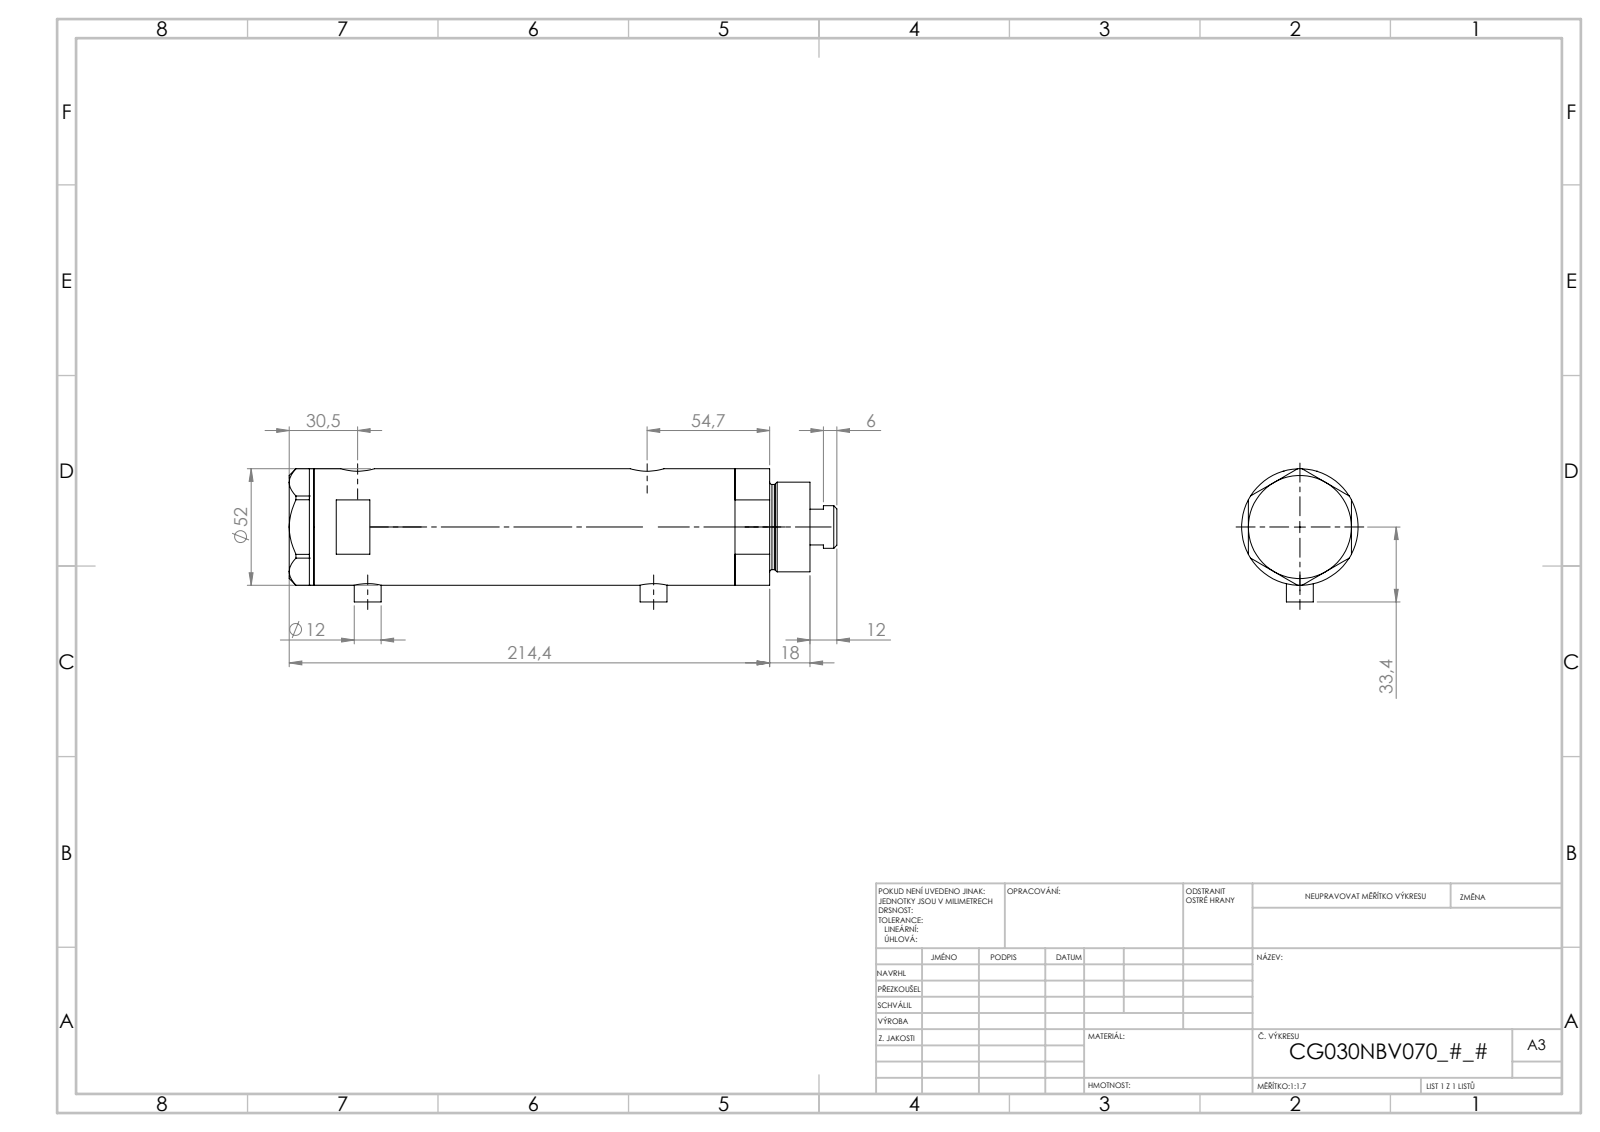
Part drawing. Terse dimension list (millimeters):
name: V270CG_FRONT; V270CG_BACK; V270CG_MIDDLE; V270CG_VC
written by: SolidWorks 2019 (CONFIG_CONTROL_DESIGN)
unit: mm
bodies: 4 solids, 134 faces (65 planar, 49 cylindrical, 20 other)
size: 244.4 × 59.4 × 52
volume: 446 635 mm³; area: 96 990 mm²
holes: 2× ⌀9.73, 2× ⌀12.5, 2× ⌀15, 1× ⌀6.5, 1× ⌀20, 1× ⌀21.5, 1× ⌀30, 1× ⌀33, 1× ⌀44
bosses: 2× ⌀12, 1× ⌀52, 1× ⌀40, 1× ⌀38, 1× ⌀19
face distances: 151.5, 23.8, 127.7, 11, 34.8, 162.5, 46, 198.9, 187.9, 164.1
hole spacings: 2.9, 4.5, 124.7, 127.6, 129.2, 132.1
